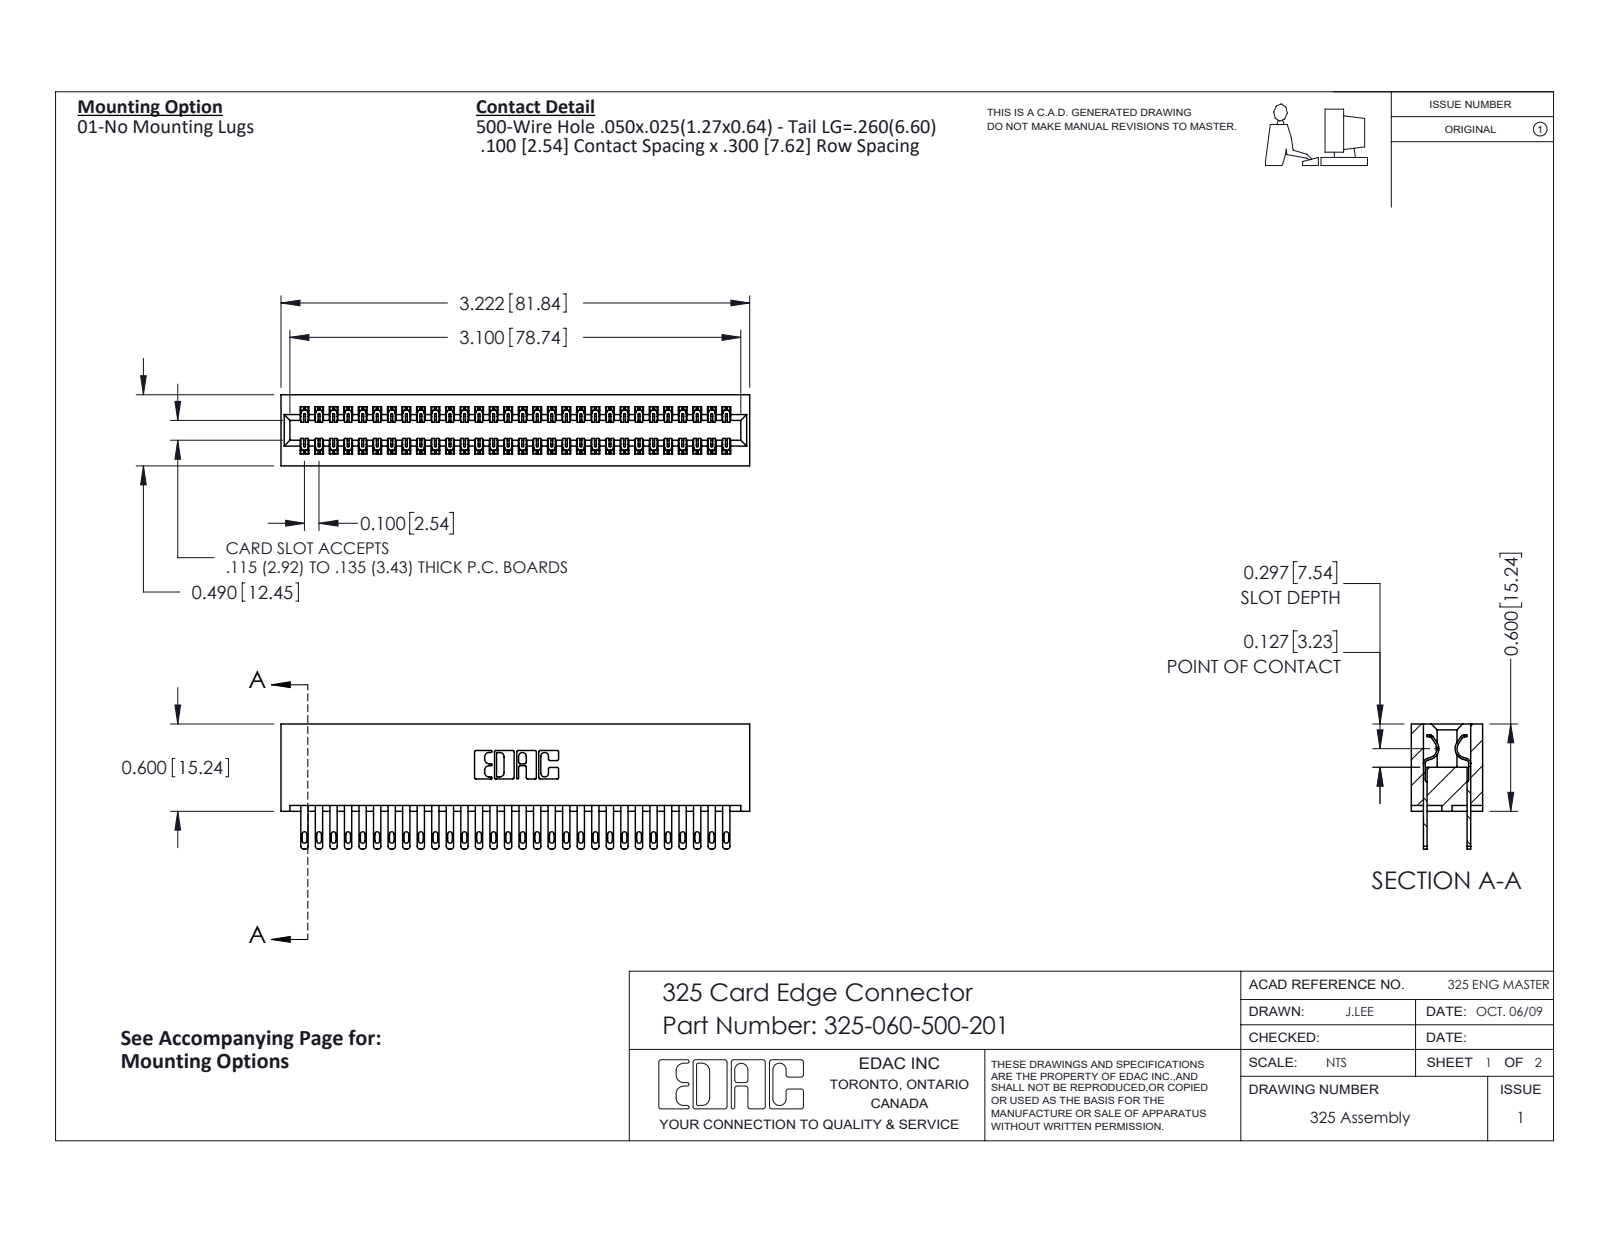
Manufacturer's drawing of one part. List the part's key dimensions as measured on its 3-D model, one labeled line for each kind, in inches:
Part name (STEP PRODUCT): 325-060-500-201; 325-292-001_325-293-100; 325 Part_Lugless
STEP written by: SolidWorks 2016 (CONFIG_CONTROL_DESIGN)
Units: inches
Bodies: 61 solids, 2986 faces (1866 planar, 1120 cylindrical, 0 other)
Overall size (bounding box): 3.222 × 0.86 × 0.49
Volume: 0.686 in³ · Surface area: 22.66 in²
Partial cylindrical surfaces — rounded edges, fillets, slot ends (radius × count): R0.006 ×90, R0.016 ×60, R0.02 ×60, R0.01 ×22, R0.007 ×6, R0.031 ×6, R0.026 ×3, R0.014 ×2
Main face-to-face distances: 0.083, 0.407, 0.3, 0.107, 0.383, 0.025, 0.325, 0.49, 0.275, 0.1
